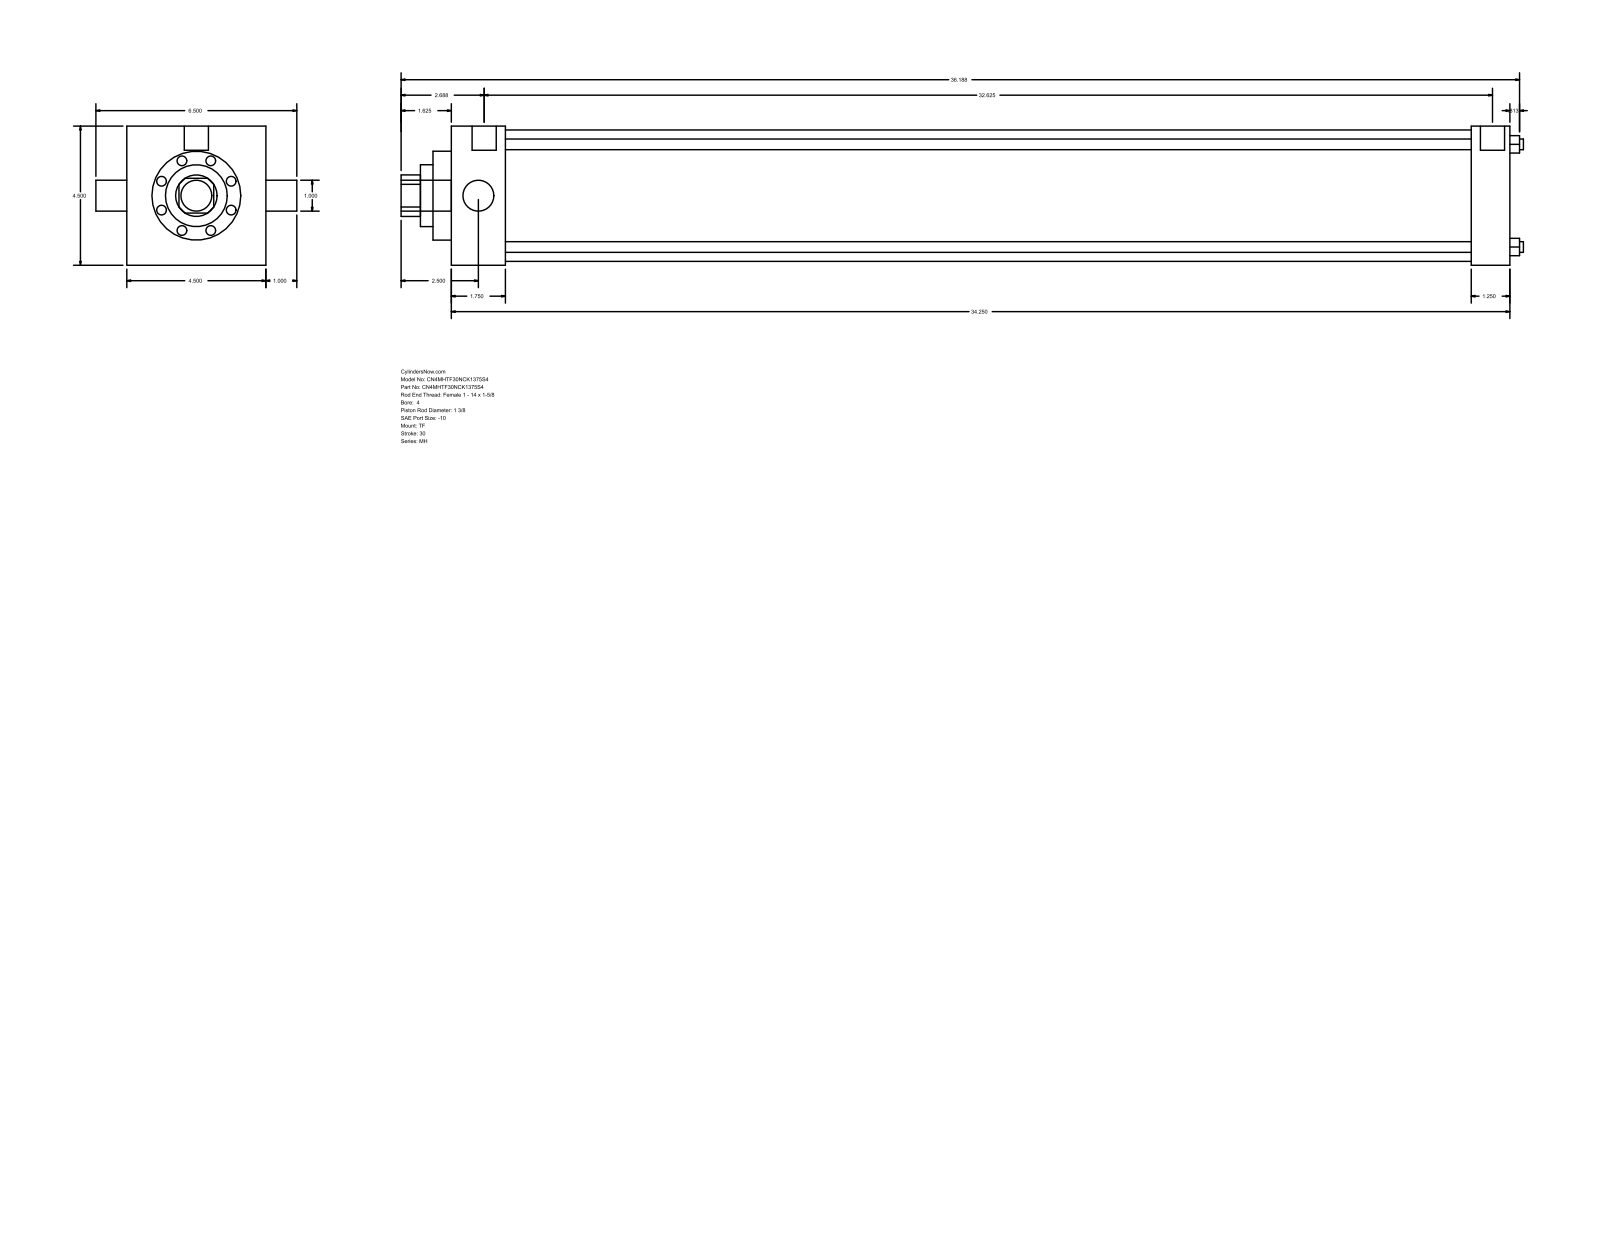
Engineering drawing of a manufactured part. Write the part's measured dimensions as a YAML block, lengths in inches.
part_name: "MH_TF__0400_1.375"
step_written_by: "GSSL Pune (CONFIG_CONTROL_DESIGN)"
units: inches
bodies: {solids: 0, faces: 86, planar: 61, cylindrical: 25, other: 0}
overall_size: [36.313, 6.5, 4.5]
round_holes:
  - {diameter: 0.345, count: 4}
  - {diameter: 1, count: 1}
  - {diameter: 1.375, count: 1}
  - {diameter: 2, count: 1}
  - {diameter: 2.875, count: 1}
  - {diameter: 4.25, count: 1}
round_bosses_or_shafts:
  - {diameter: 0.344, count: 3}
  - {diameter: 0.781, count: 2}
  - {diameter: 1, count: 1}
partial_cylinders:
  - {radius: 0.672, count: 1}
face_to_face_distances: [4.5, 34.25, 1.75, 32.5, 33, 31.25, 1.25, 0.594, 2.344, 33.594]
hole_center_spacings: [2.347, 3.32, 4.695]
